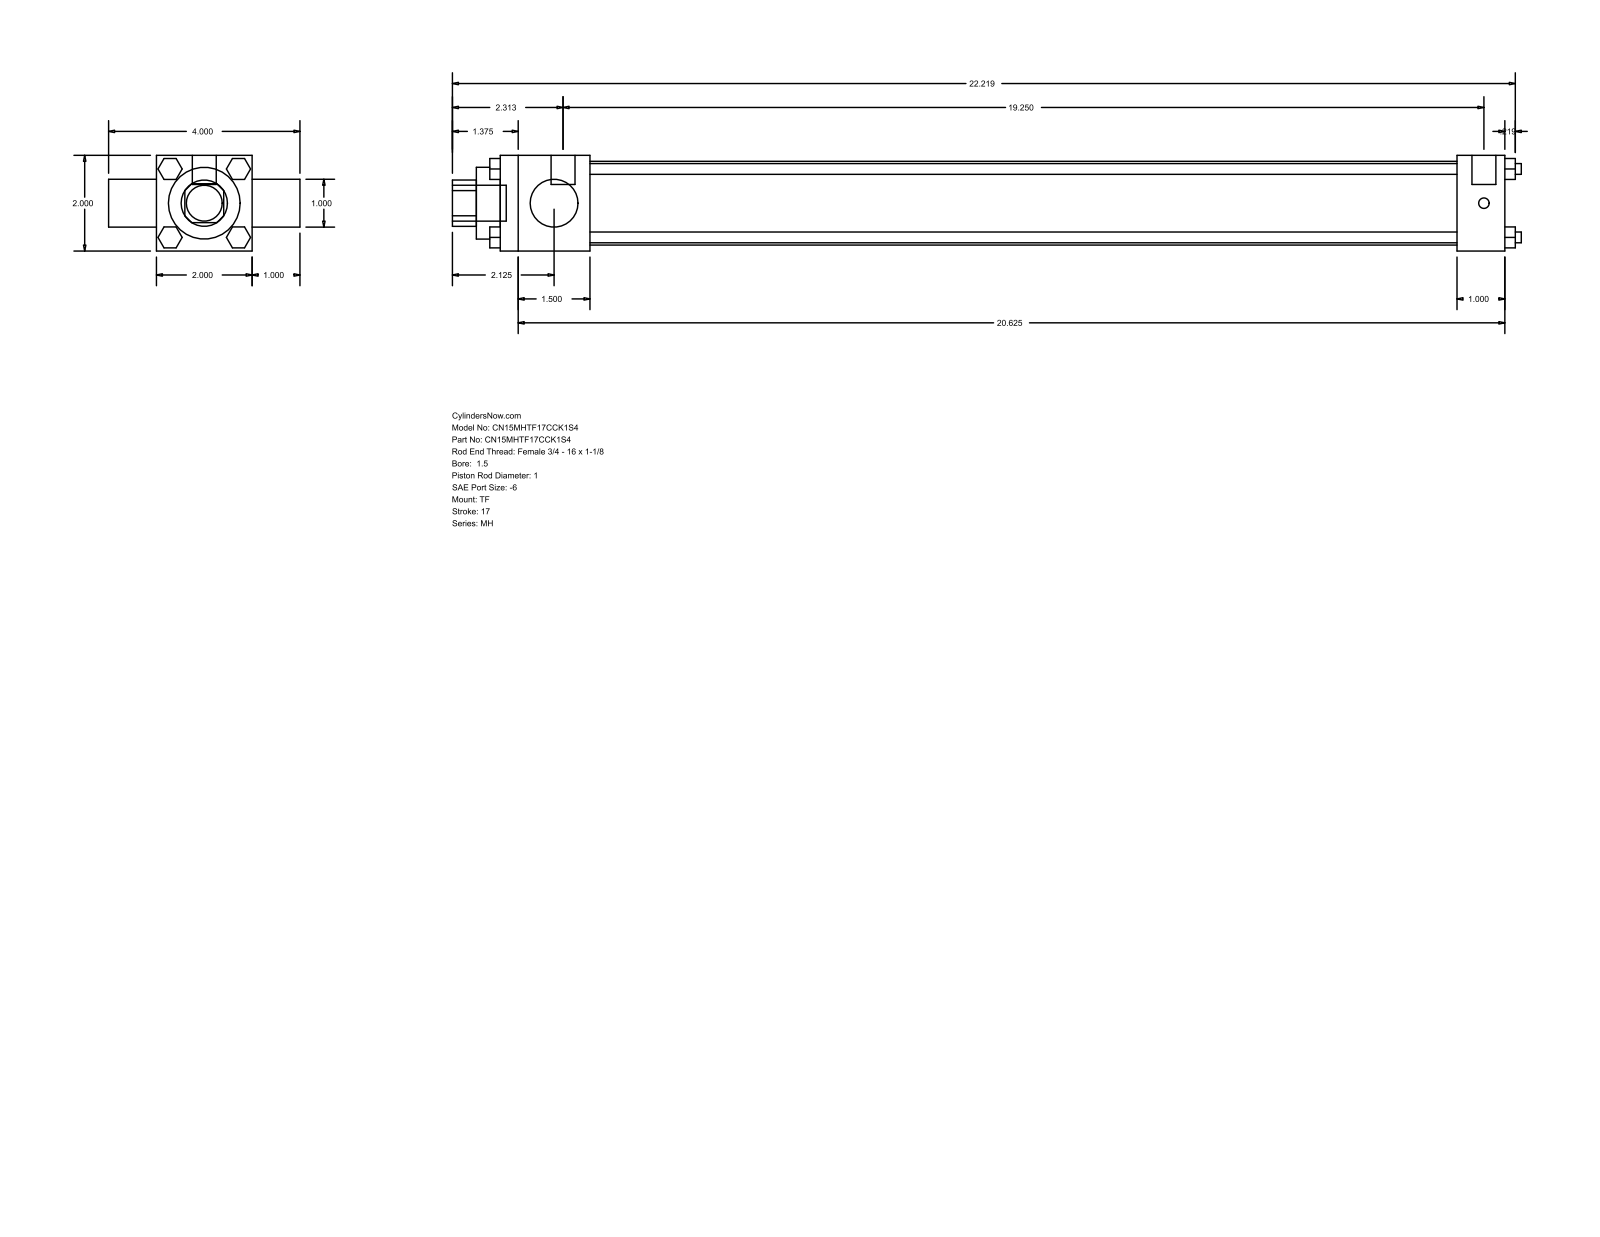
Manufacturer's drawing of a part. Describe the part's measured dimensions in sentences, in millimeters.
The part is named "MH_TF__0150_1". Its 3-D file was written by "GSSL Pune (CONFIG_CONTROL_DESIGN)". It is 0 solids with 120 faces: 92 planar, 28 cylindrical and 0 other. Overall it measures 567.53 by 101.6 by 50.8 millimeters. Round holes: 2 of diameter 25.4, 1 of diameter 38.1, 1 of diameter 44.45. Round bosses or shafts: 4 of diameter 5.71, 3 of diameter 5.56, 2 of diameter 12.7, 1 of diameter 19.05. Partial cylindrical surfaces (rounded edges, fillets, slot ends): 1 of radius 12.29. The main face-to-face distances are 50.8, 25.4, 533.4, 76.2, 47.63, 485.77, 508, 460.37, 538.96, 12.7.
